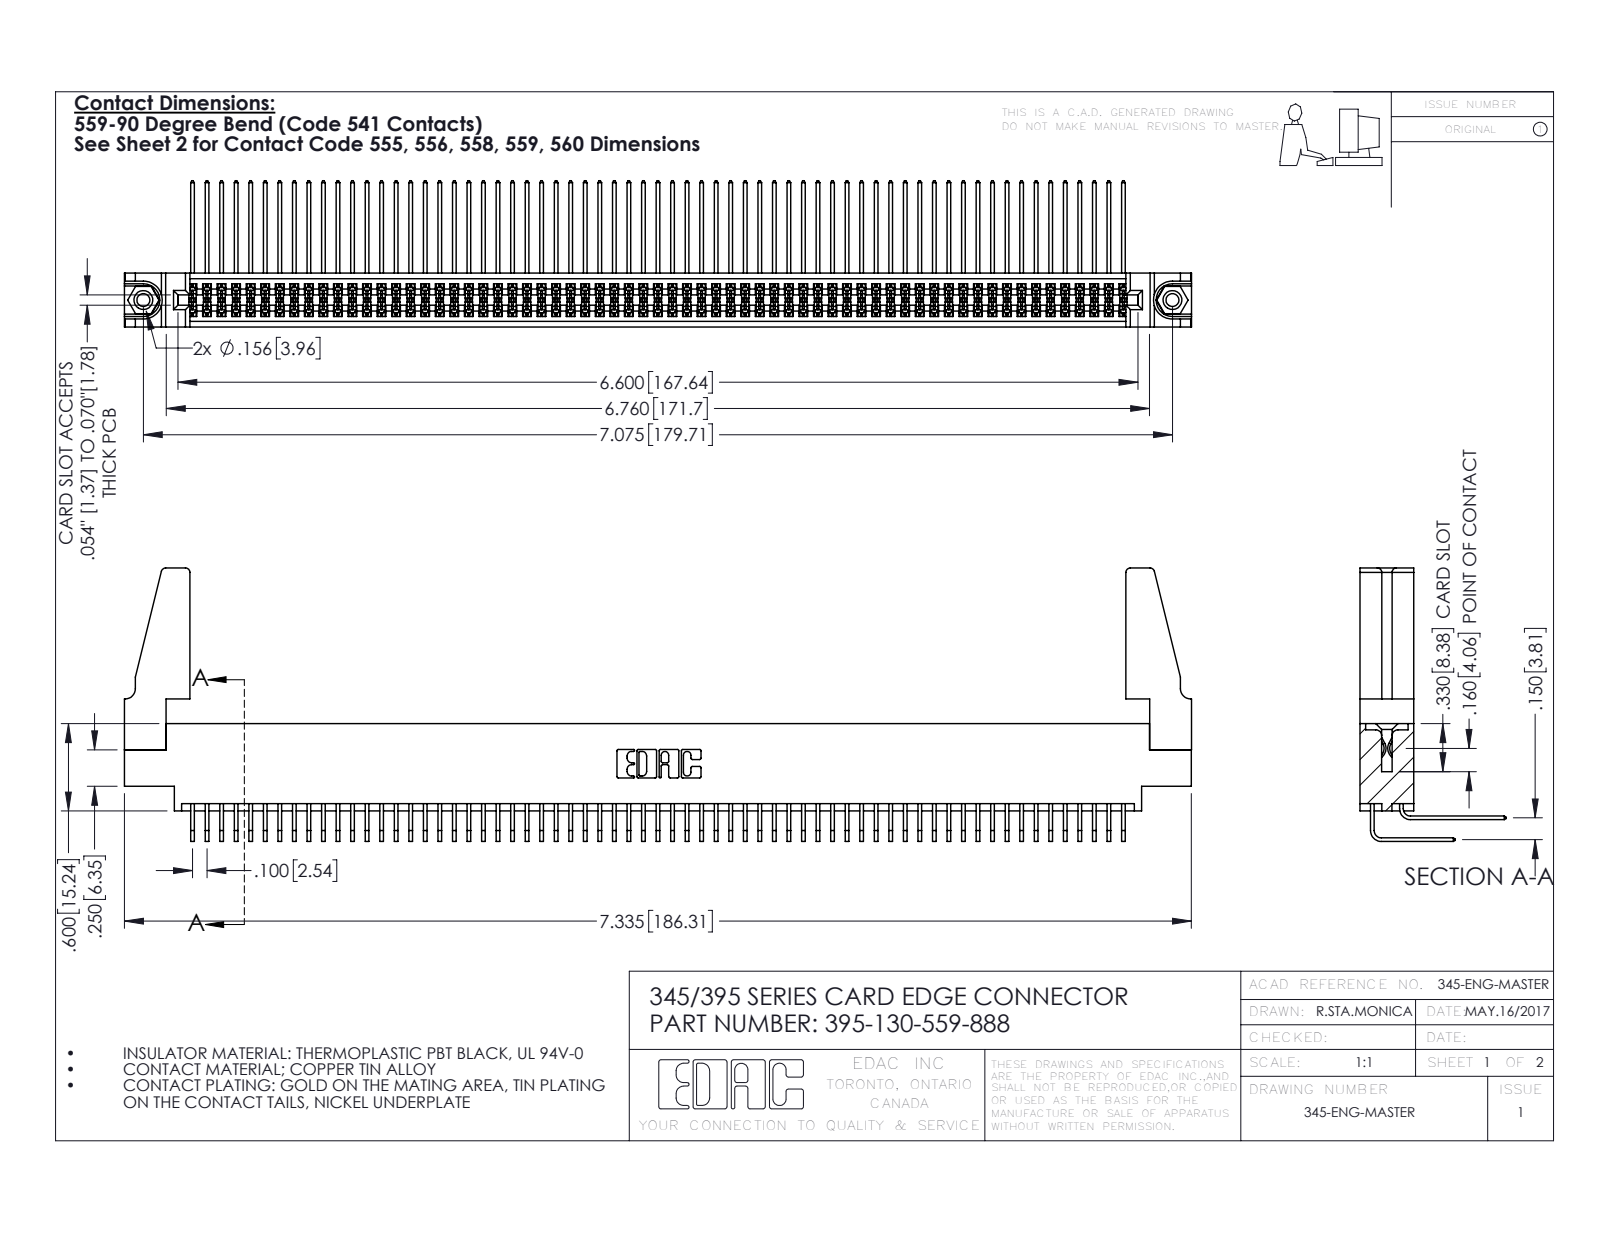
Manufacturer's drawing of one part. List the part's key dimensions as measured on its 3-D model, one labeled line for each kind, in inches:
Part name (STEP PRODUCT): 345-220-078_345-220-088; 345-250-001_345-250-001-102; 345 Part_0.170 Offset - 0.156 Dia-TH; 345-292-001_559 Tail - 2 (+2 more)
STEP written by: SolidWorks 2016 (CONFIG_CONTROL_DESIGN)
Units: inches
Bodies: 135 solids, 7014 faces (4706 planar, 2292 cylindrical, 16 other)
Overall size (bounding box): 7.336 × 1.879 × 1.005
Volume: 1.355 in³ · Surface area: 54.64 in²
Round holes (diameter × count): ⌀0.089 ×2, ⌀0.125 ×2, ⌀0.156 ×2, ⌀0.064 ×1
Round bosses / shafts (diameter × count): ⌀0.155 ×2
Partial cylindrical surfaces — rounded edges, fillets, slot ends (radius × count): R0.006 ×196, R0.01 ×22, R0.03 ×8, R0.007 ×6, R0.031 ×6, R0.026 ×3, R0.014 ×2, R0.019 ×2
Main face-to-face distances: 0.072, 0.298, 0.37, 0.2, 0.098, 0.272, 0.025, 0.225, 0.15, 0.175
Hole centre spacings: 0.27, 6.839, 7.075
